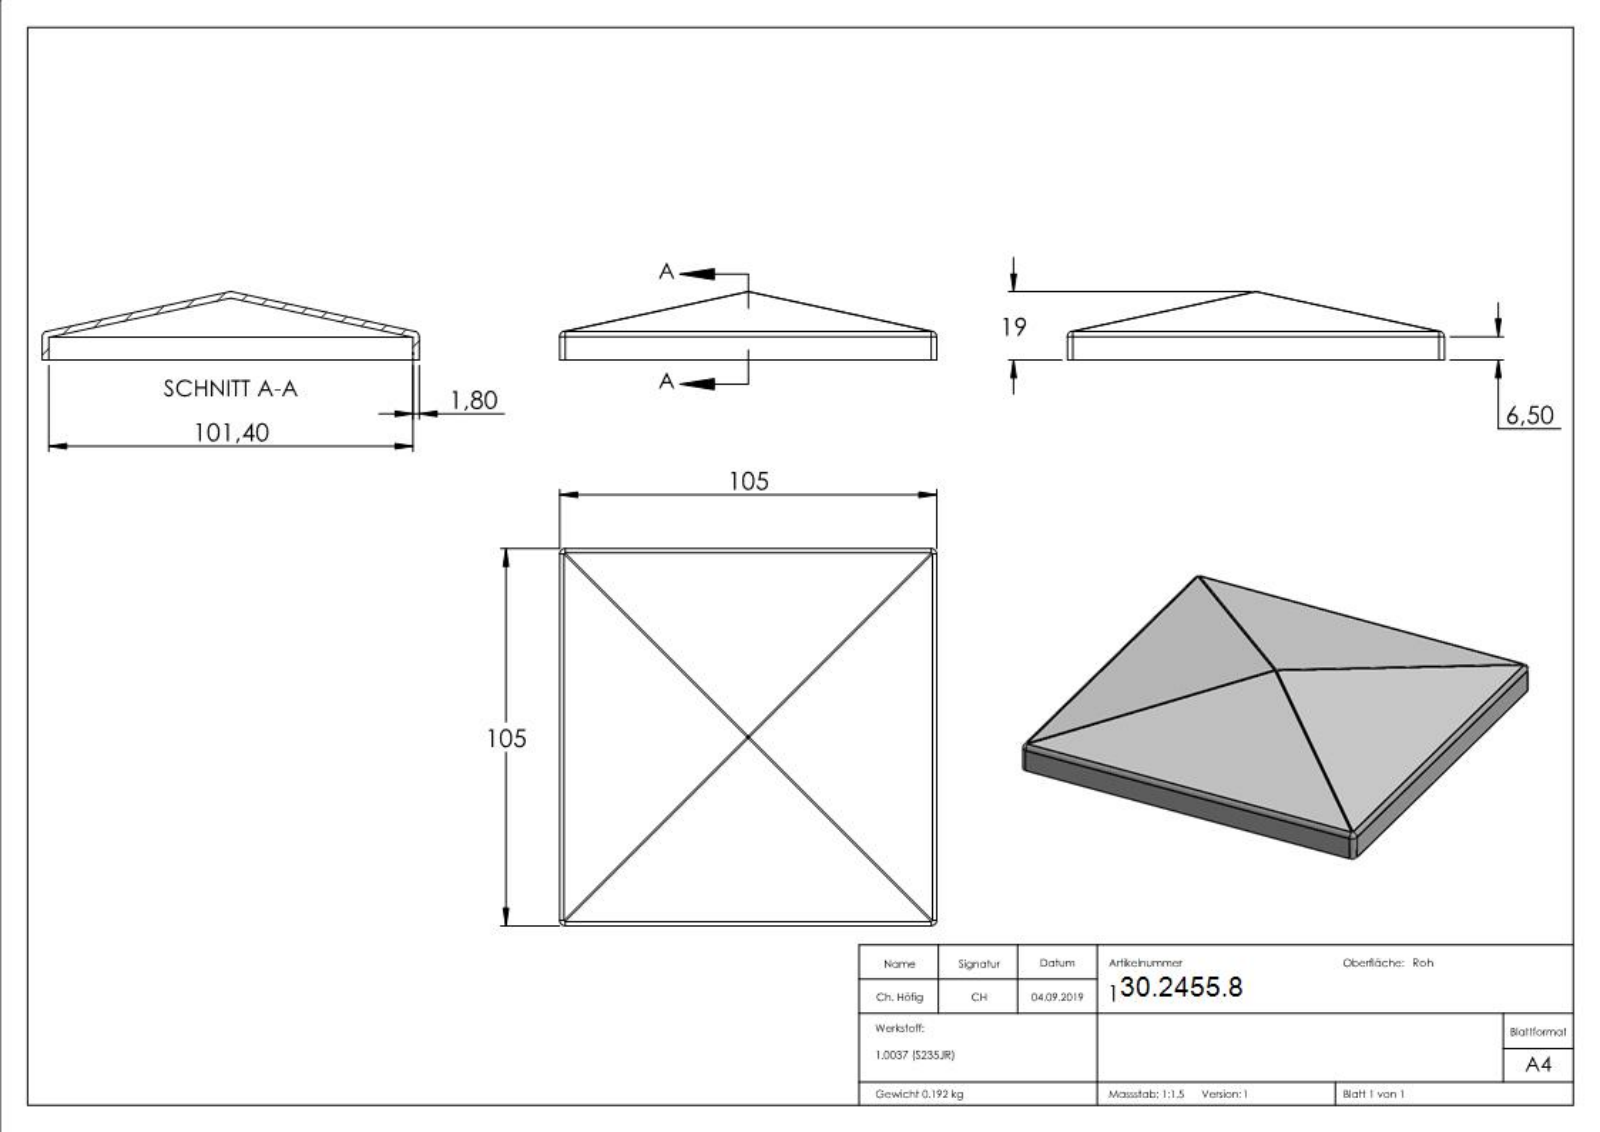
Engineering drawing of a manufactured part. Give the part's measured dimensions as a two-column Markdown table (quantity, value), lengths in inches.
| quantity | value |
| --- | --- |
| part name | 165-100 |
| STEP written by | SolidWorks 2015 (CONFIG_CONTROL_DESIGN) |
| units | inches |
| bodies | 1 solid, 220 faces (117 planar, 12 cylindrical, 91 other) |
| overall size | 4.134 × 4.134 × 0.748 |
| volume | 1.505 in³ |
| surface area | 43.62 in² |
| partial cylindrical surfaces (radius × count) | 0.059 × 12 |
| main face-to-face distances | 0.071, 4.063, 4.134, 3.992, 0.067, 3.996, 4.067, 0.303, 0.447, 0.144 |
